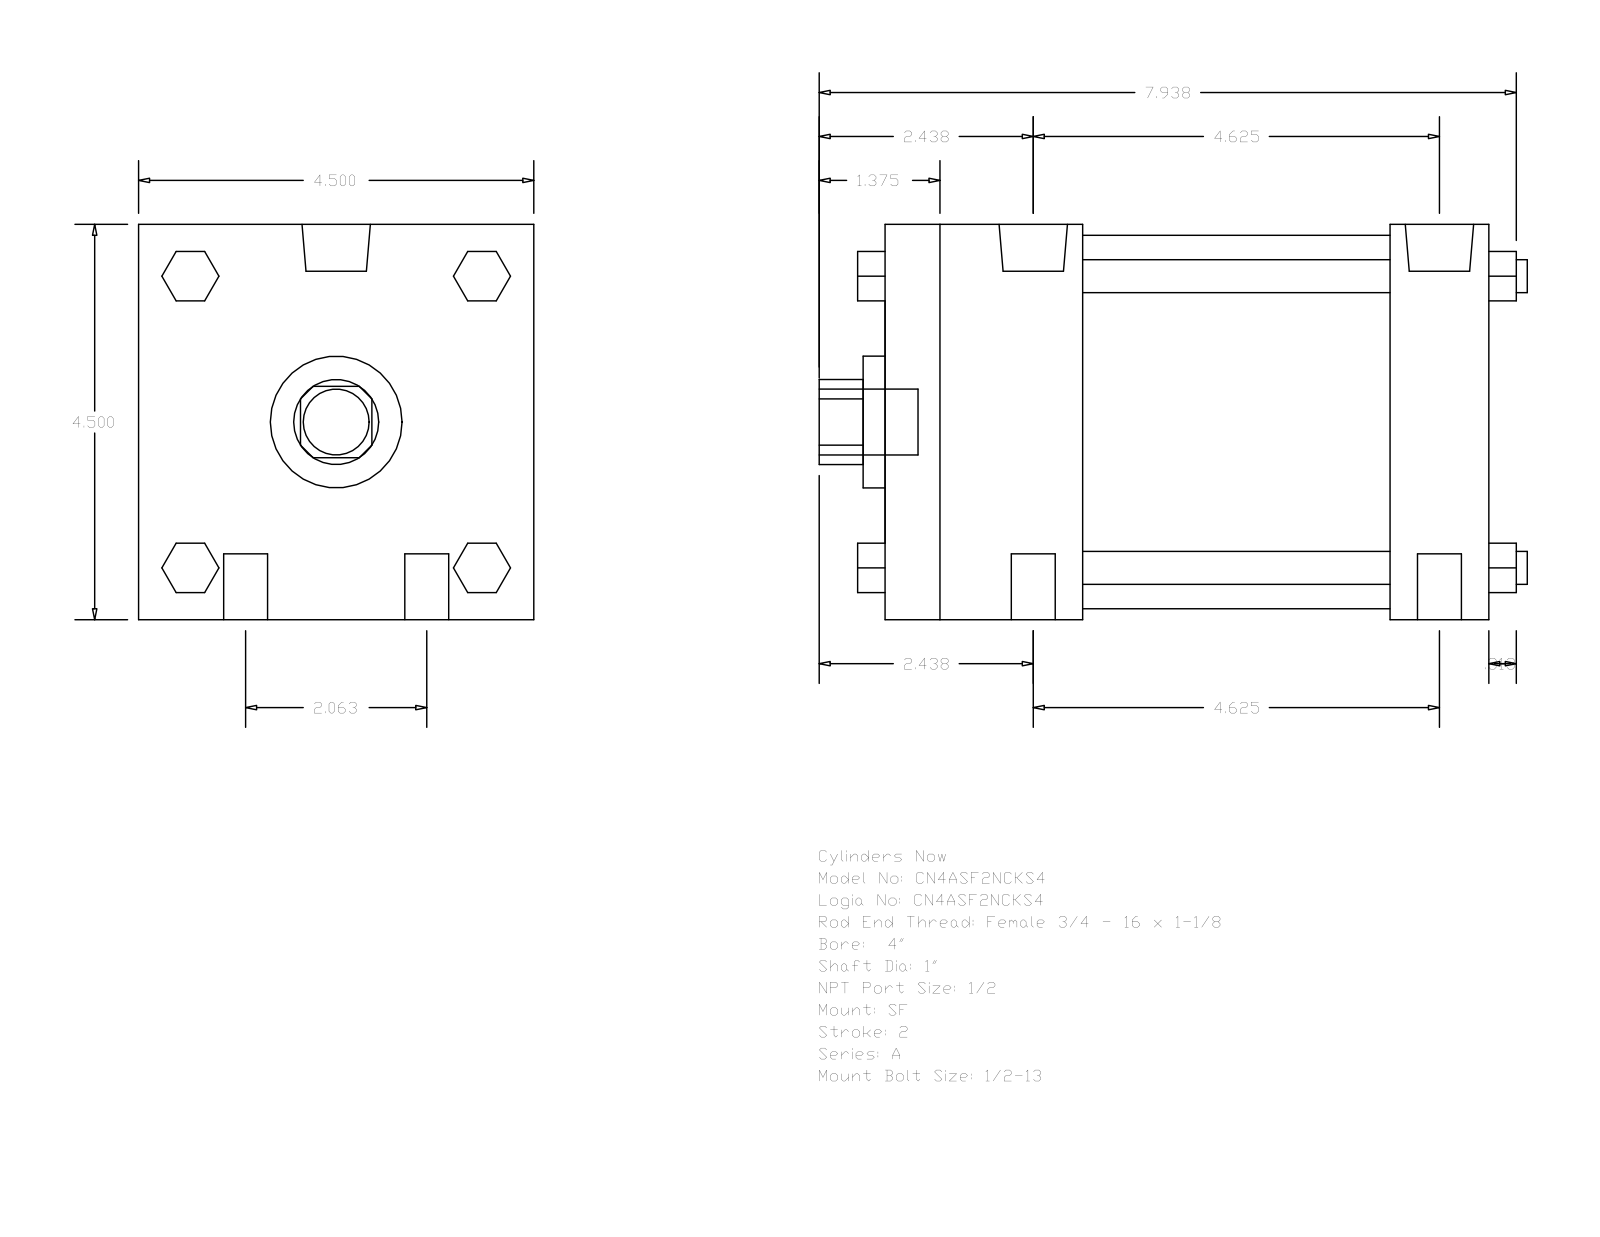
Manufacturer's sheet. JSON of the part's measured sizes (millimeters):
{"part_name": "A_SF__0400_1", "step_written_by": "GSSL Pune (CONFIG_CONTROL_DESIGN)", "units": "millimeters", "bodies": {"solids": 0, "faces": 124, "planar": 94, "cylindrical": 30, "other": 0}, "overall_size": [204.79, 114.3, 114.3], "round_holes": [[25.4, 1], [38.1, 1], [107.95, 1]], "round_bosses_or_shafts": [[12.7, 4], [9.53, 4], [19.77, 2], [8.73, 2], [19.05, 1]], "partial_cylinders_radius": [[12.29, 1]], "face_to_face_distances": [114.3, 174.63, 146.05, 28.58, 57.15, 88.9, 117.48, 14.29, 42.16, 73.03]}
